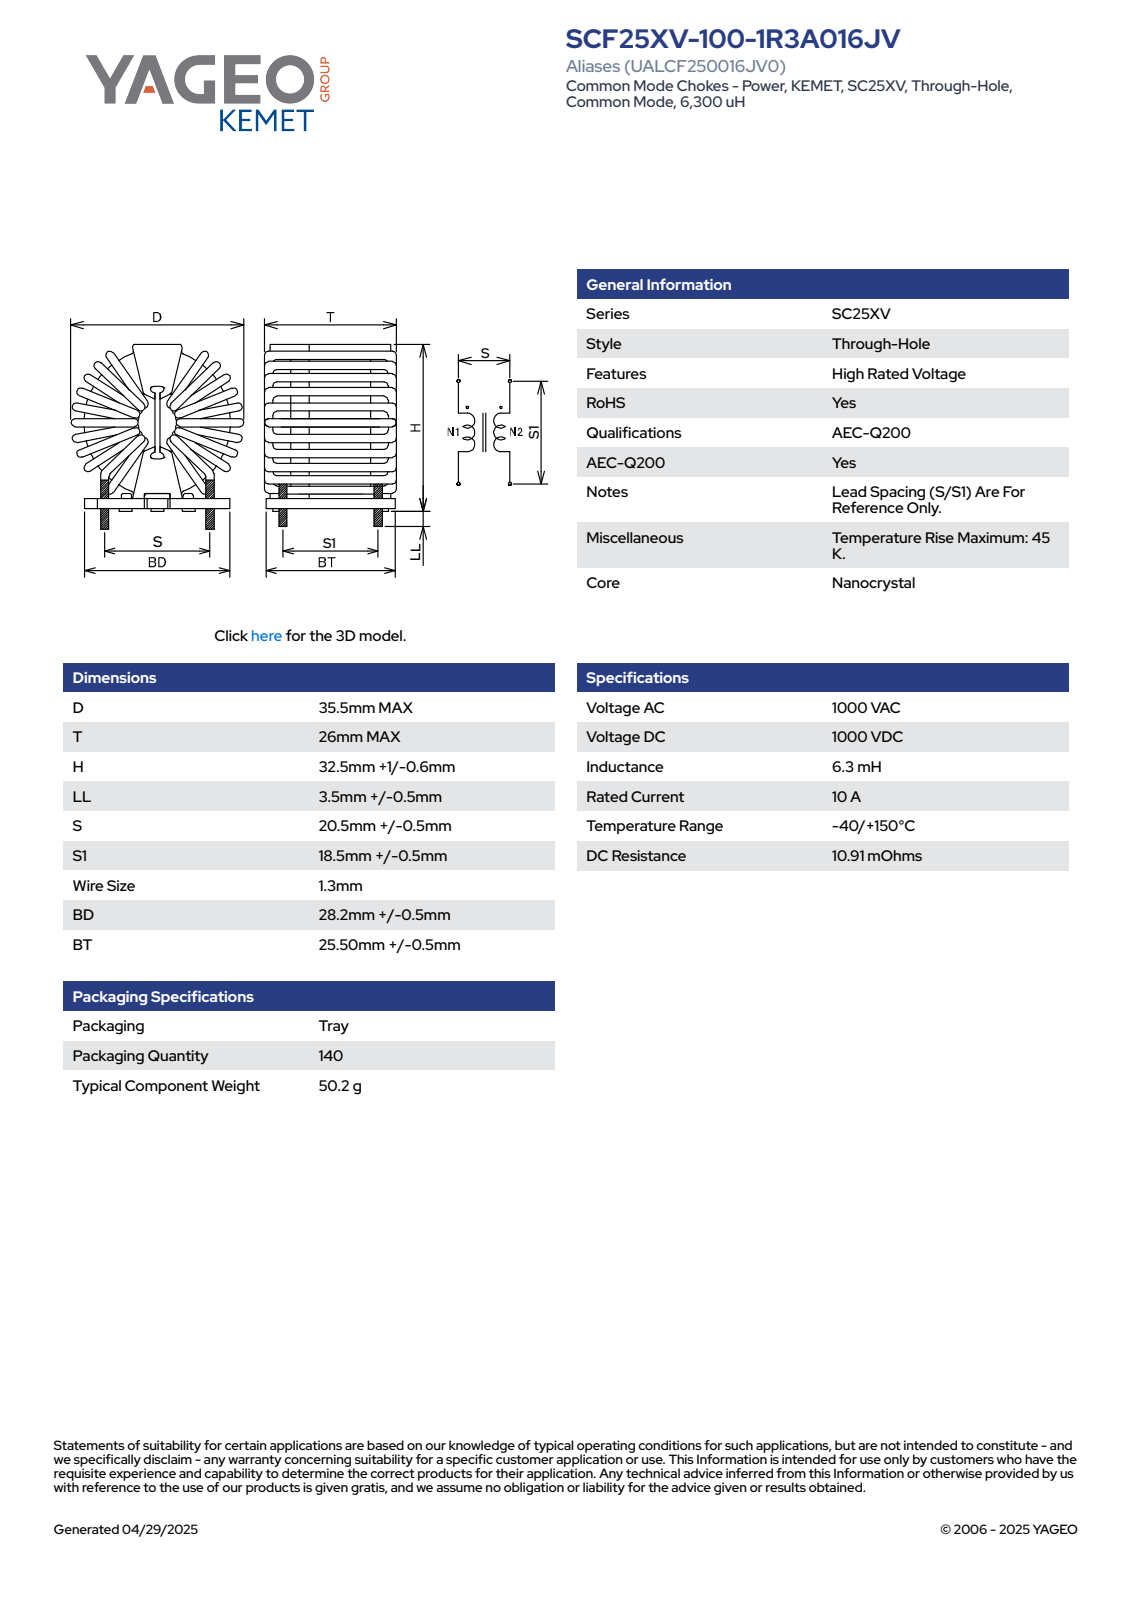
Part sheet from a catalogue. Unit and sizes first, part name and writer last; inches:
Units: inches
Overall size (bounding box): 1.457 × 1.398 × 1.024
Round holes (diameter × count): ⌀0.059 ×6, ⌀0.067 ×4, ⌀0.118 ×4, ⌀0.047 ×2
Round bosses / shafts (diameter × count): ⌀0.051 ×4, ⌀0.098 ×3
Partial cylindrical surfaces — rounded edges, fillets, slot ends (radius × count): R0.02 ×34, R0.012 ×16, R0.051 ×16, R0.03 ×4, R0.059 ×4, R0.132 ×4, R0.039 ×3, R0.748 ×2
Main face-to-face distances: 0.039, 1.024, 0.079, 0.02, 0.059, 0.049, 0.974, 0.197, 0.728, 0.925
Hole centre spacings: 0.125, 0.746, 0.835, 1.113, 0.02, 0.269, 0.274, 0.283
Volume: 1.236 in³ · Surface area: 16.09 in²
Bodies: 1 solid, 581 faces (281 planar, 196 cylindrical, 104 other)
Part name (STEP PRODUCT): 簡易版_SC25XV-100-1R3A016JV
STEP written by: SolidWorks 2022 (AUTOMOTIVE_DESIGN)
